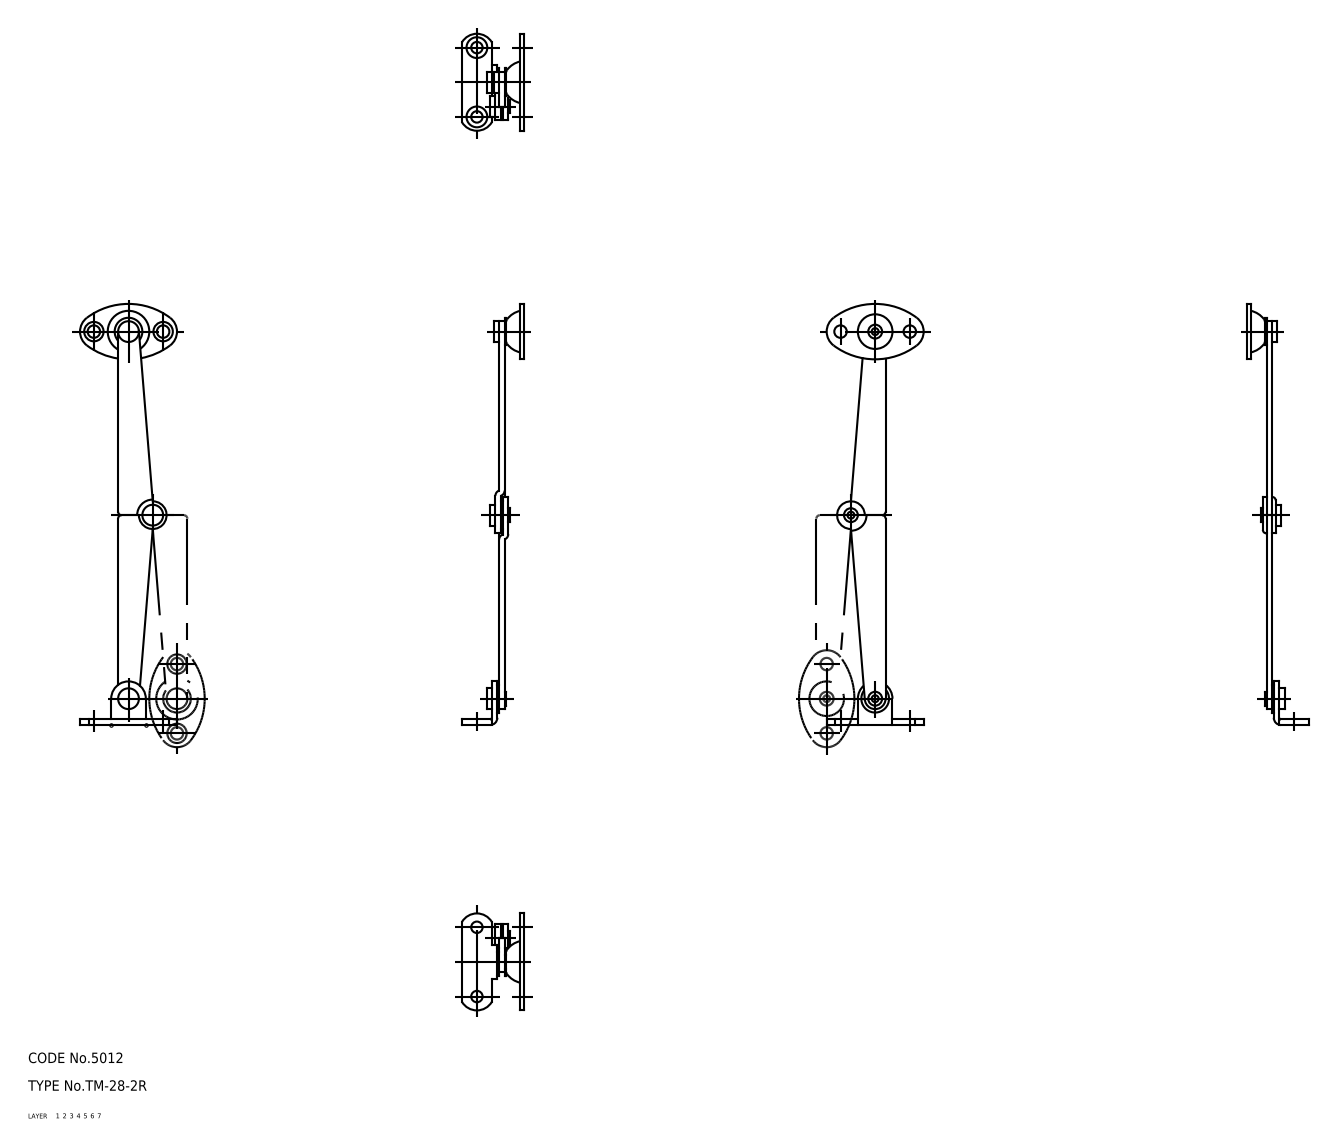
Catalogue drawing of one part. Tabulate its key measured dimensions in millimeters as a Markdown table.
| quantity | value |
| --- | --- |
| part name | washer_mr-2; washer_mr-1; rivet_1_mr-1; arm_mr-1 (+7 more) |
| STEP written by | CADfix (AUTOMOTIVE_DESIGN) |
| units | millimeters |
| bodies | 10 solids, 125 faces (0 planar, 0 cylindrical, 125 other) |
| overall size | 121.6 × 28 × 17.8 |
| volume | 2 740 mm³ |
| surface area | 4 900 mm² |
